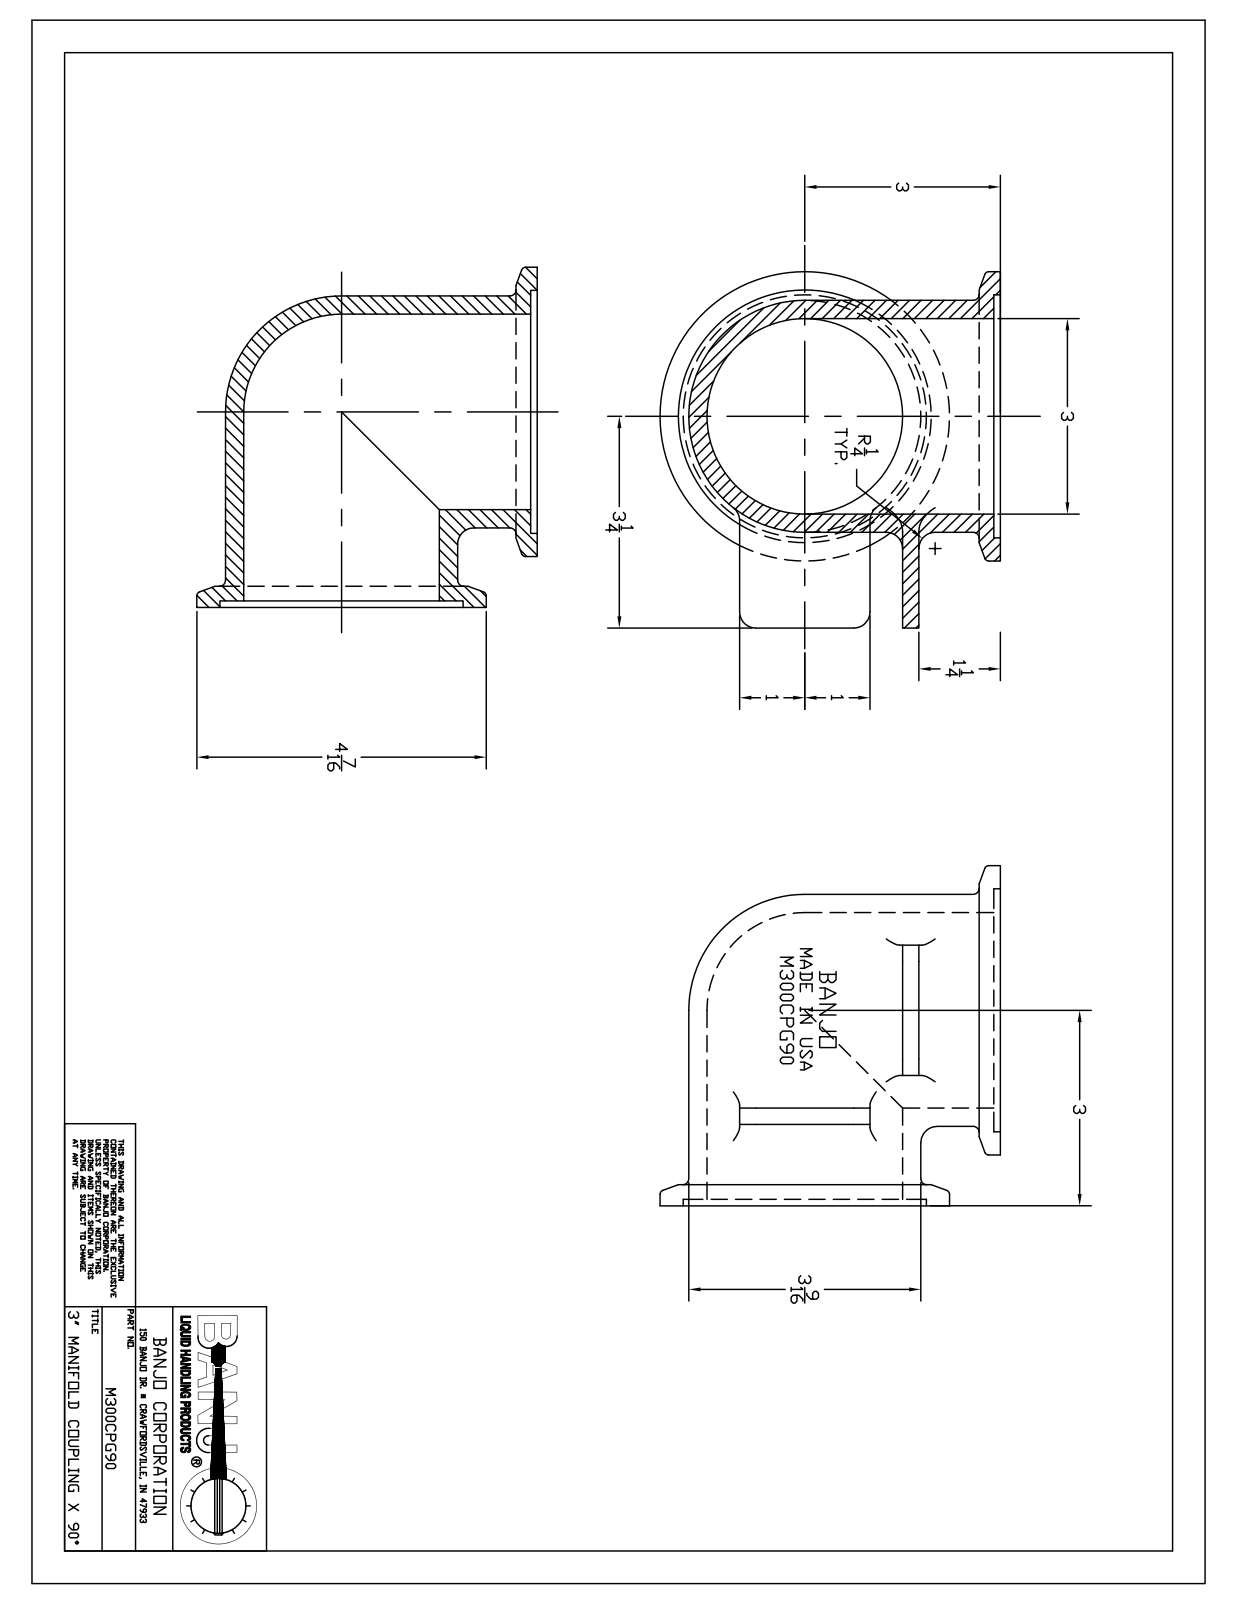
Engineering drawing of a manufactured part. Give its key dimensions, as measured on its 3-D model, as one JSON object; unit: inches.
{"part_name": "M300CPG90", "step_written_by": "Autodesk Inventor 2012 (AUTOMOTIVE_DESIGN)", "units": "inches", "bodies": {"solids": 1, "faces": 472, "planar": 179, "cylindrical": 69, "other": 224}, "overall_size": [5.47, 5.22, 5.22], "volume_in3": 21.1, "surface_area_in2": 156.9, "round_holes": [[3, 2], [3.73, 2]], "round_bosses_or_shafts": [[4.44, 2], [3.56, 2]], "partial_cylinders_radius": [[0.06, 12], [0.25, 8], [1.8, 2]], "face_to_face_distances": [0.1, 1.4, 1.5, 1.15, 1.25, 0.25, 2, 0.5, 0.75, 1.9]}
